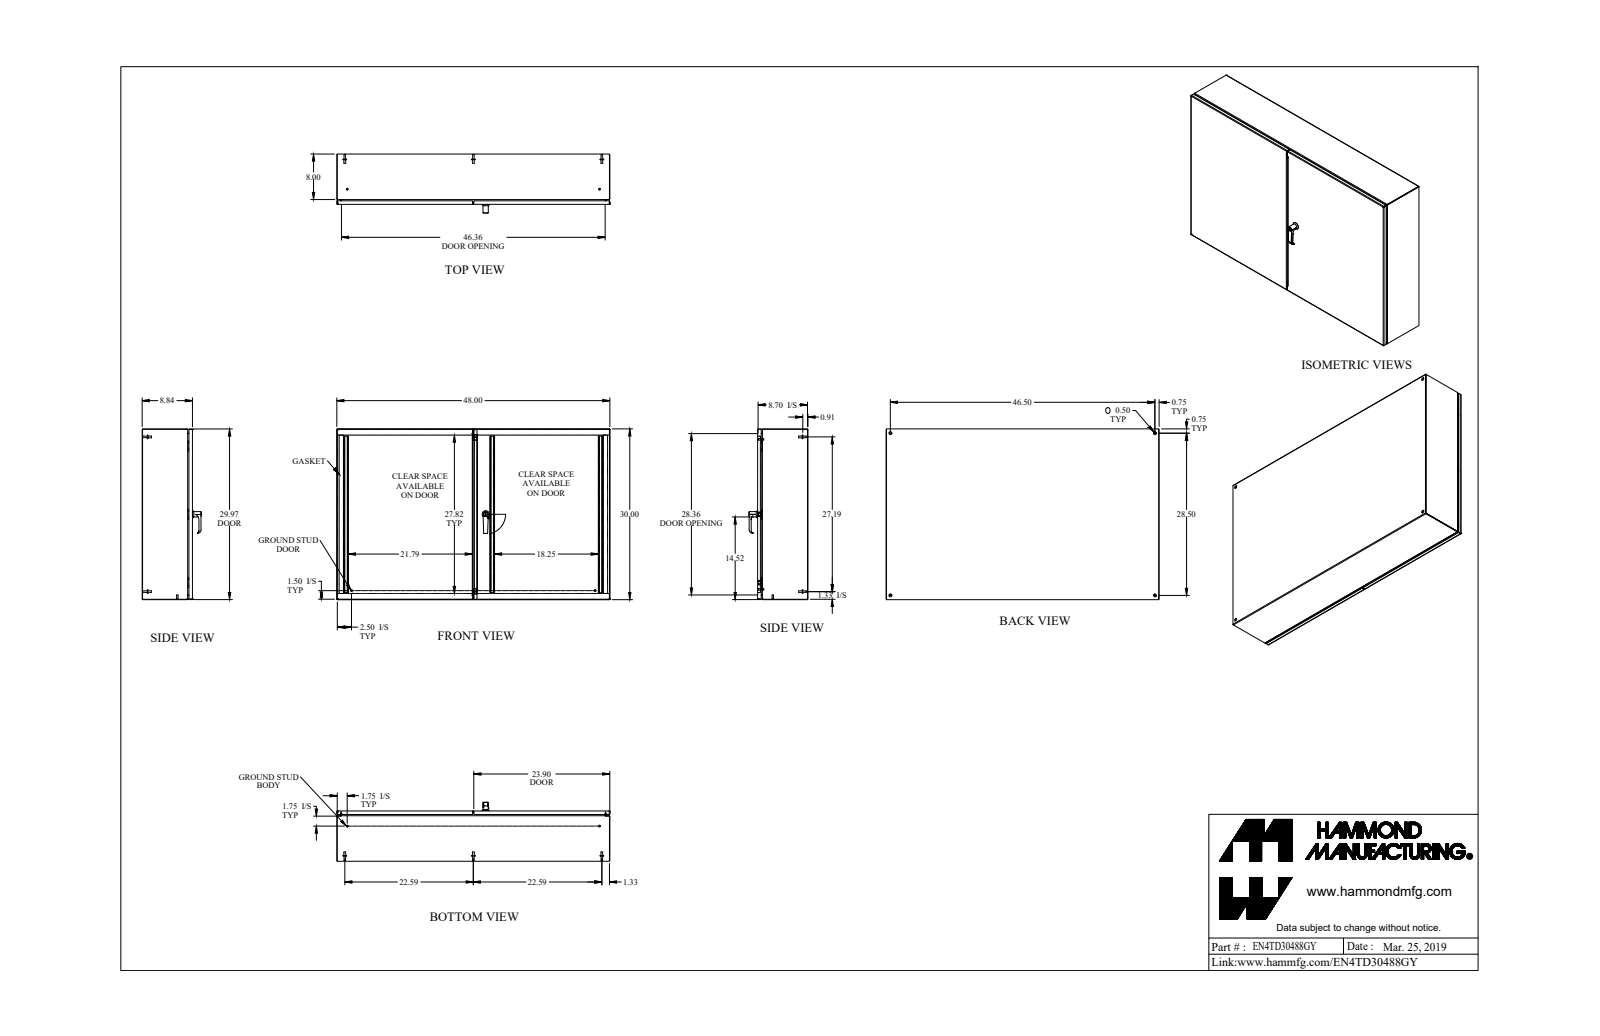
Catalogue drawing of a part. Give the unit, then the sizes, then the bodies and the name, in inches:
Units: inches
Overall size (bounding box): 48 × 30 × 10.372
Round holes (diameter × count): ⌀0.196 ×5, ⌀0.176 ×4, ⌀0.265 ×4, ⌀0.5 ×4, ⌀0.24 ×3, ⌀0.242 ×3, ⌀0.172 ×2, ⌀0.25 ×2, ⌀0.256 ×2, ⌀0.26 ×2, ⌀0.313 ×2, ⌀0.394 ×2
Round bosses / shafts (diameter × count): ⌀0.25 ×12, ⌀0.313 ×8, ⌀0.625 ×6, ⌀0.27 ×6, ⌀0.51 ×4, ⌀0.281 ×4, ⌀0.156 ×4, ⌀0.75 ×3
Partial cylindrical surfaces — rounded edges, fillets, slot ends (radius × count): R0.036 ×26, R0.108 ×26, R0.094 ×20, R0.043 ×18, R0.081 ×18, R0.063 ×17, R0.02 ×16, R0.062 ×16
Main face-to-face distances: 0.072, 8.77, 8.698, 8.842, 29.928, 47.928, 29.856, 30, 47.856, 48
Hole centre spacings: 0.786, 13.188, 20.798, 25.447, 25.752, 28.5, 29.139, 46.5
Volume: 376.4 in³ · Surface area: 9 845 in²
Bodies: 85 solids, 2139 faces (955 planar, 790 cylindrical, 394 other)
Part name (STEP PRODUCT): EN4TD30488GY
STEP written by: SolidWorks 2018 (AUTOMOTIVE_DESIGN)
